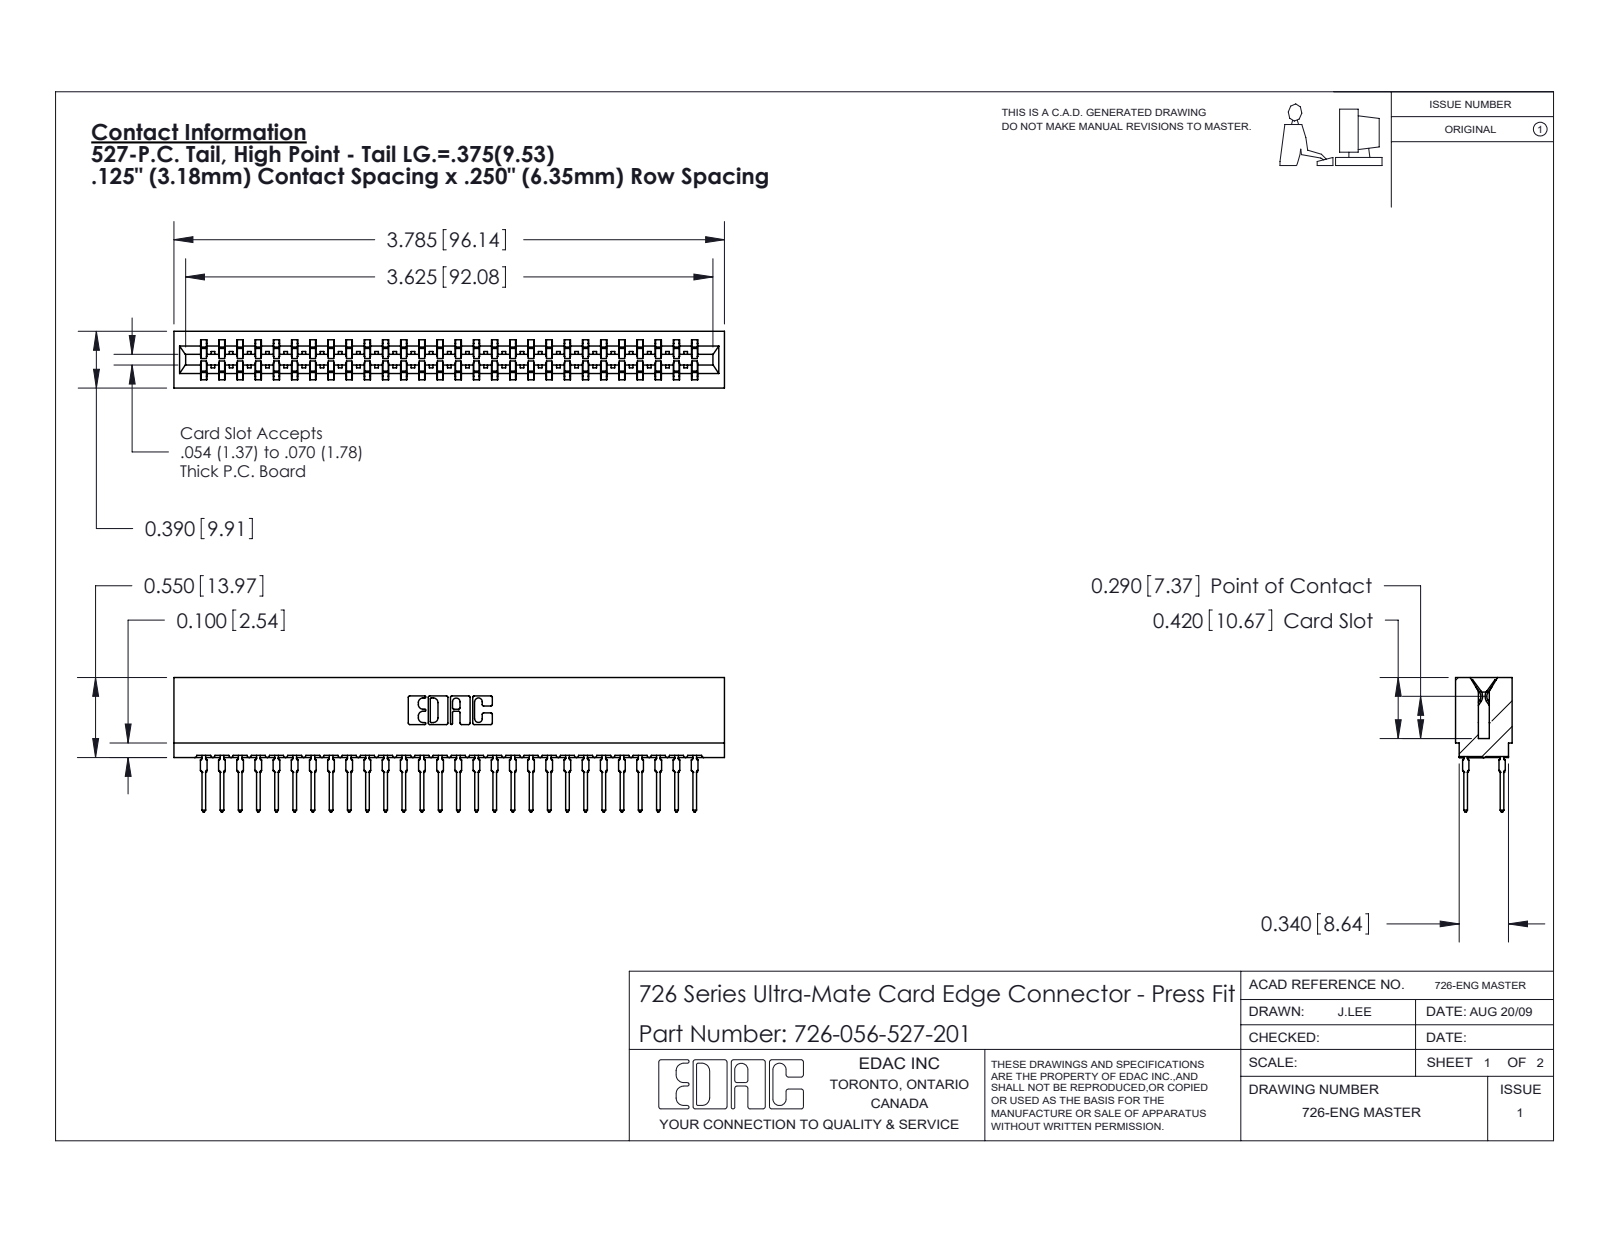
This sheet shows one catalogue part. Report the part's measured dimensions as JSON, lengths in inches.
{"part_name": "726-056-527-201; 746-292-001_527; 726 Part_.515 Slot Depth - 01", "step_written_by": "SolidWorks 2020 (CONFIG_CONTROL_DESIGN)", "units": "inches", "bodies": {"solids": 57, "faces": 5109, "planar": 2631, "cylindrical": 1022, "other": 1456}, "overall_size": [3.785, 0.924, 0.39], "volume_in3": 0.55, "surface_area_in2": 23.58, "partial_cylinders_radius": [[0.021, 112], [0.015, 29], [0.01, 22], [0.005, 8], [0.011, 8], [0.007, 6], [0.031, 6], [0.026, 3]], "face_to_face_distances": [0.057, 0.333, 0.25, 0.025, 0.307, 0.39, 0.083, 0.275, 0.5, 0.365]}
